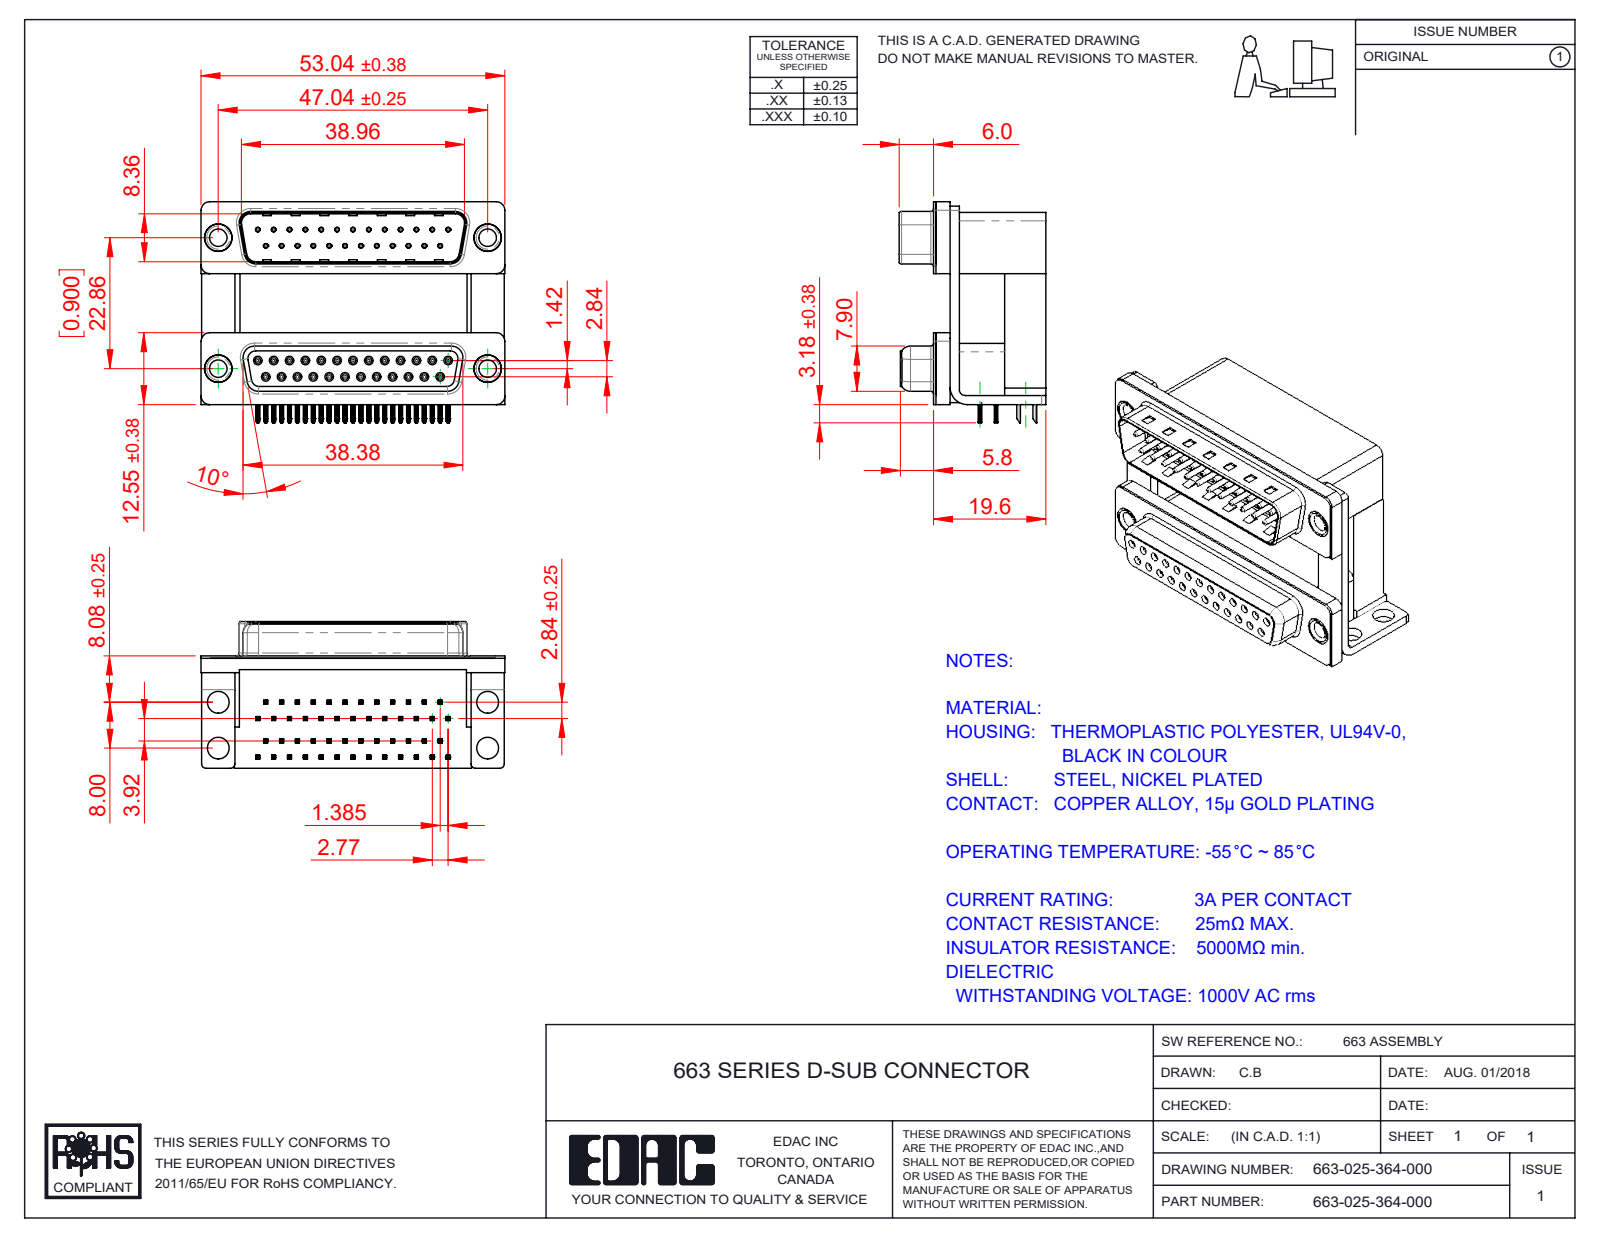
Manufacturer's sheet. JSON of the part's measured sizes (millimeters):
{"part_name": "663 Housing Lower_25 Contacts; 663 Shell Plug_25 Contacts; 663 Mounting Bracket_NoneH; 663 Contact Top Lower (+8 more)", "step_written_by": "SolidWorks 2020 (CONFIG_CONTROL_DESIGN)", "units": "millimeters", "bodies": {"solids": 61, "faces": 6119, "planar": 3257, "cylindrical": 1507, "other": 1355}, "overall_size": [53.04, 38.59, 25.6], "volume_mm3": 23668, "surface_area_mm2": 24839, "round_holes": [[0.8, 50], [0.35, 25], [0.9, 25], [3.05, 4], [3.5, 4], [3.8, 4], [4, 4], [4.8, 4], [5, 4]], "round_bosses_or_shafts": [[1.2, 25], [0.75, 25], [4.9, 4], [4.75, 4], [3.85, 4]], "partial_cylinders_radius": [[0.1, 200], [0.15, 100], [0.25, 100], [0.12, 50], [0.35, 50], [0.34, 25], [1.5, 14], [0.28, 12]], "face_to_face_distances": [19.2, 12, 7.2, 0.4, 10.7, 16.7, 9.5, 2.5, 22.86, 12.4], "hole_center_spacings": [3.16, 2.77, 5.54, 11.08, 8.31, 5.03, 13.85, 7.48]}
